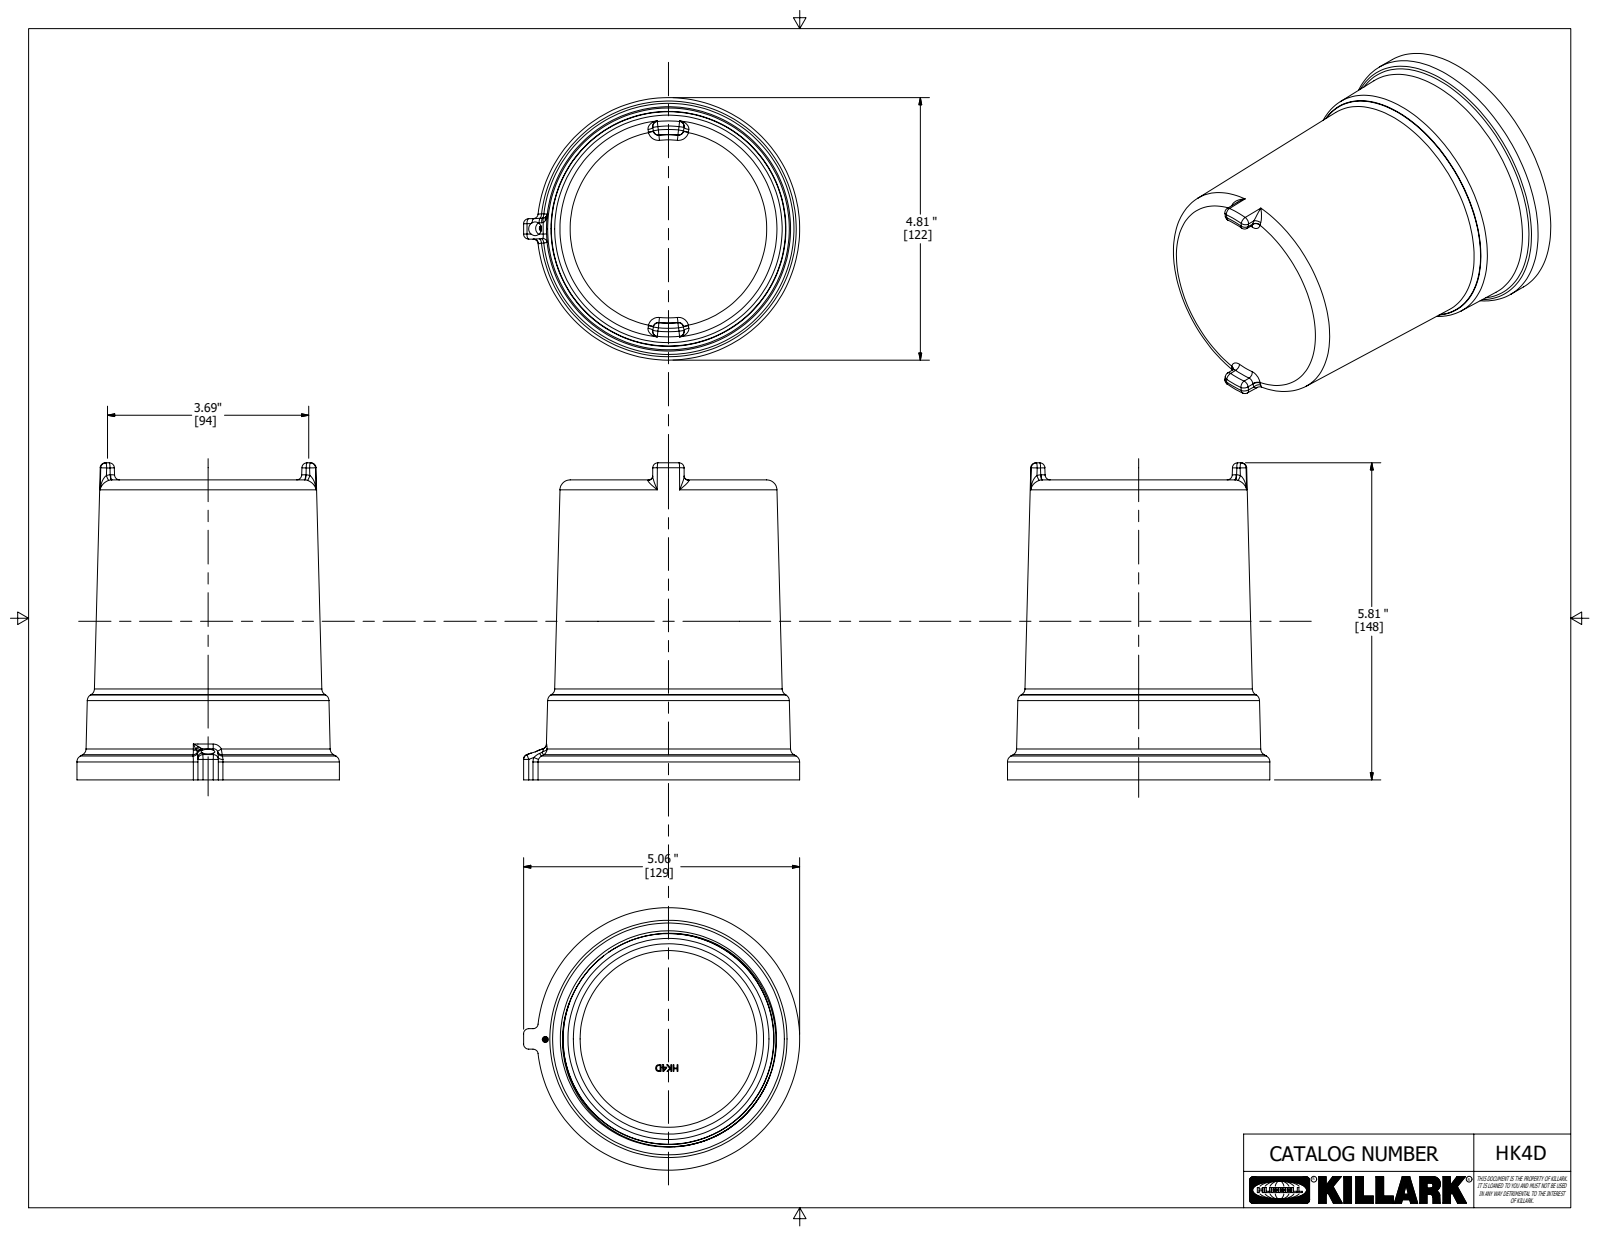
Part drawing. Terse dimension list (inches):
name: 16048ABAM
written by: Autodesk Inventor 2020 (AUTOMOTIVE_DESIGN)
unit: in
bodies: 3 solids, 761 faces (395 planar, 37 cylindrical, 329 other)
size: 5.813 × 5.063 × 4.813
volume: 22.57 in³; area: 198 in²
holes: 1× ⌀0.063, 1× ⌀0.104, 1× ⌀0.25, 1× ⌀3.862, 1× ⌀3.965, 1× ⌀4.25
bosses: 1× ⌀4.813, 1× ⌀0.104
rounds: 8× R0.094
face distances: 0.25, 5.5, 5.25, 0.188, 5.062, 5.312, 1.375, 1.187, 3.875, 4.125
